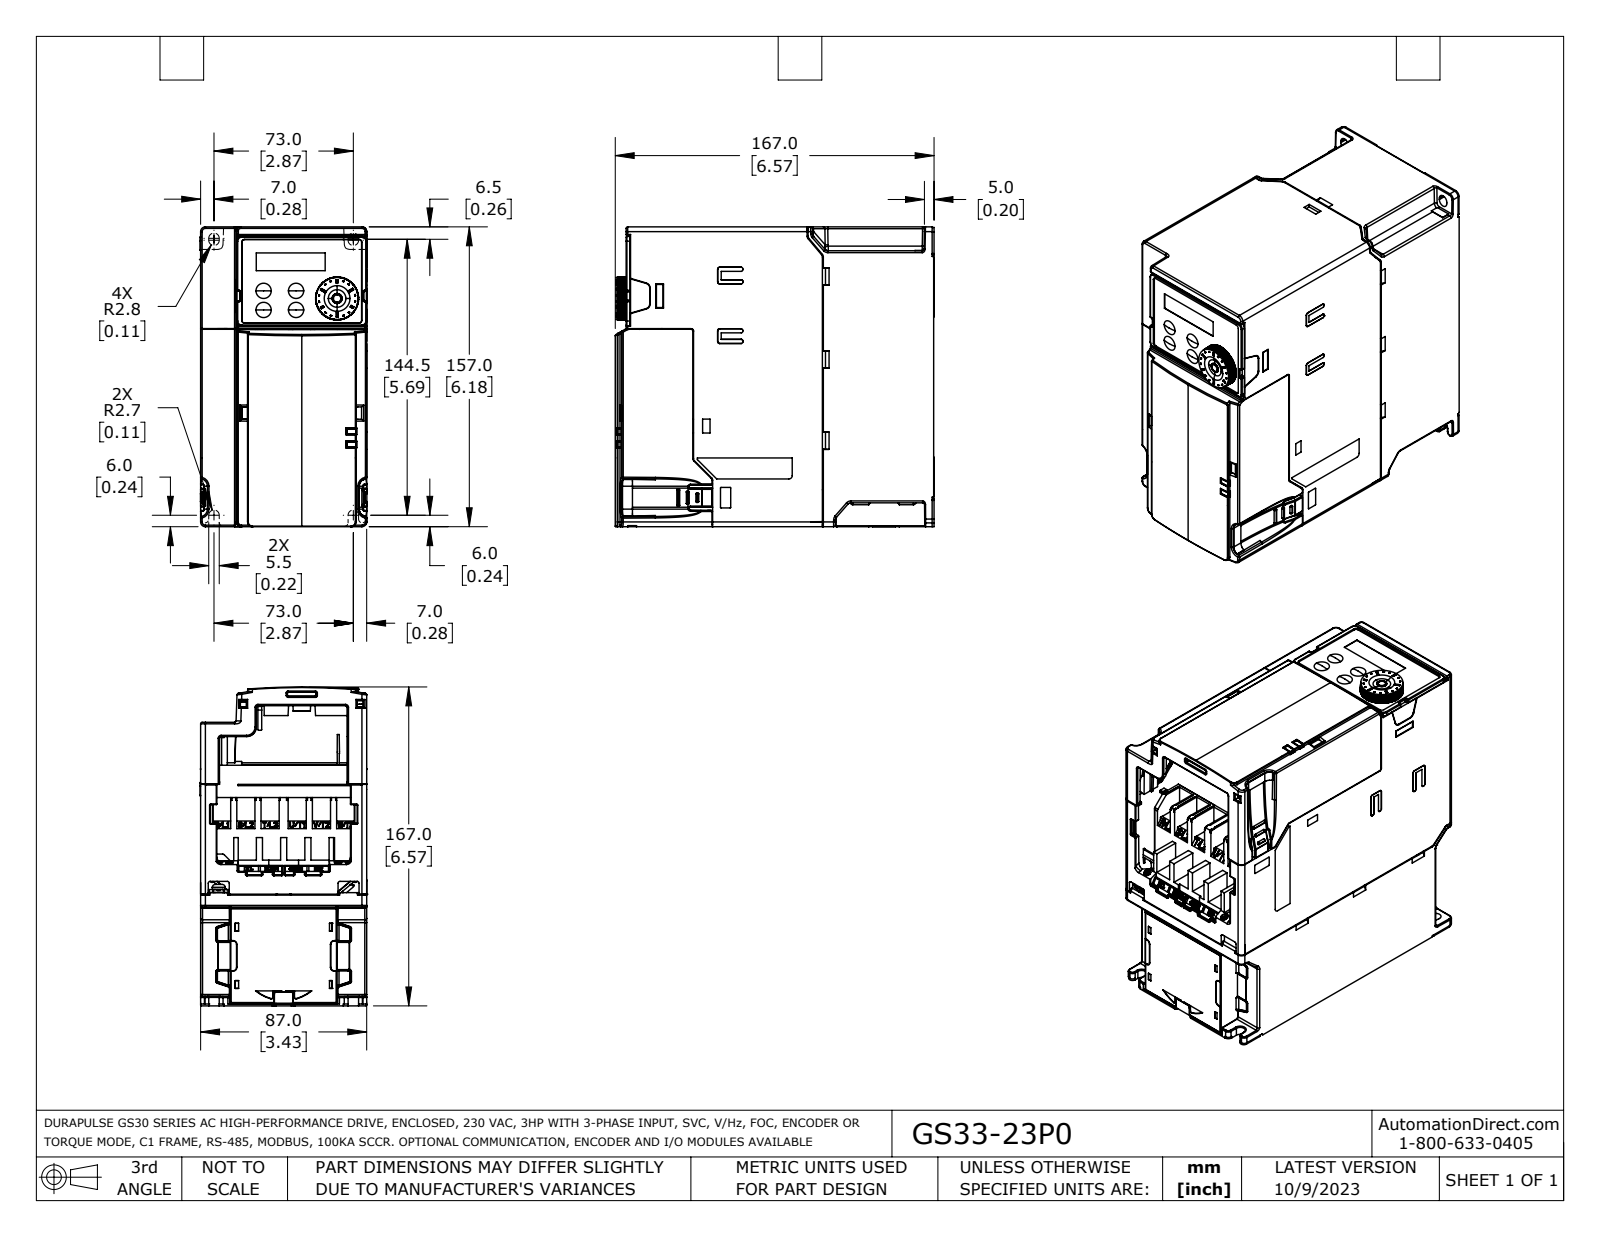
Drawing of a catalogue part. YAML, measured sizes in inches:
part_name: "VFD-MH300-C1-PD-3D02 NC red1 sr1 surfrep1 Bott TB n FG ONLY 1 sr1bc ext1B wo fg ac comb wiht D1 Mod ska5coord top Bcb sr1xyb fxt coord"
step_written_by: "SolidWorks 2021 (AUTOMOTIVE_DESIGN)"
units: inches
bodies: {solids: 7, faces: 4300, planar: 2193, cylindrical: 1183, other: 924}
overall_size: [6.575, 6.181, 3.44]
volume: 30.29
surface_area: 383.2
round_holes:
  - {diameter: 0.098, count: 4}
  - {diameter: 0.157, count: 4}
  - {diameter: 0.11, count: 2}
  - {diameter: 0.709, count: 1}
  - {diameter: 0.76, count: 1}
round_bosses_or_shafts:
  - {diameter: 0.268, count: 1}
  - {diameter: 0.157, count: 1}
partial_cylinders:
  - {radius: 0.02, count: 219}
  - {radius: 0.008, count: 164}
  - {radius: 0.012, count: 163}
  - {radius: 0.039, count: 97}
  - {radius: 0.079, count: 45}
  - {radius: 0.031, count: 35}
  - {radius: 0.016, count: 23}
  - {radius: 0.028, count: 17}
face_to_face_distances: [3.425, 0.039, 0.059, 3.386, 0.098, 0.121, 3.304, 3.265, 0.082, 0.354]
hole_center_spacings: [0.596, 2.588, 4.735, 5.247, 5.32, 5.754, 0.236, 0.493]
